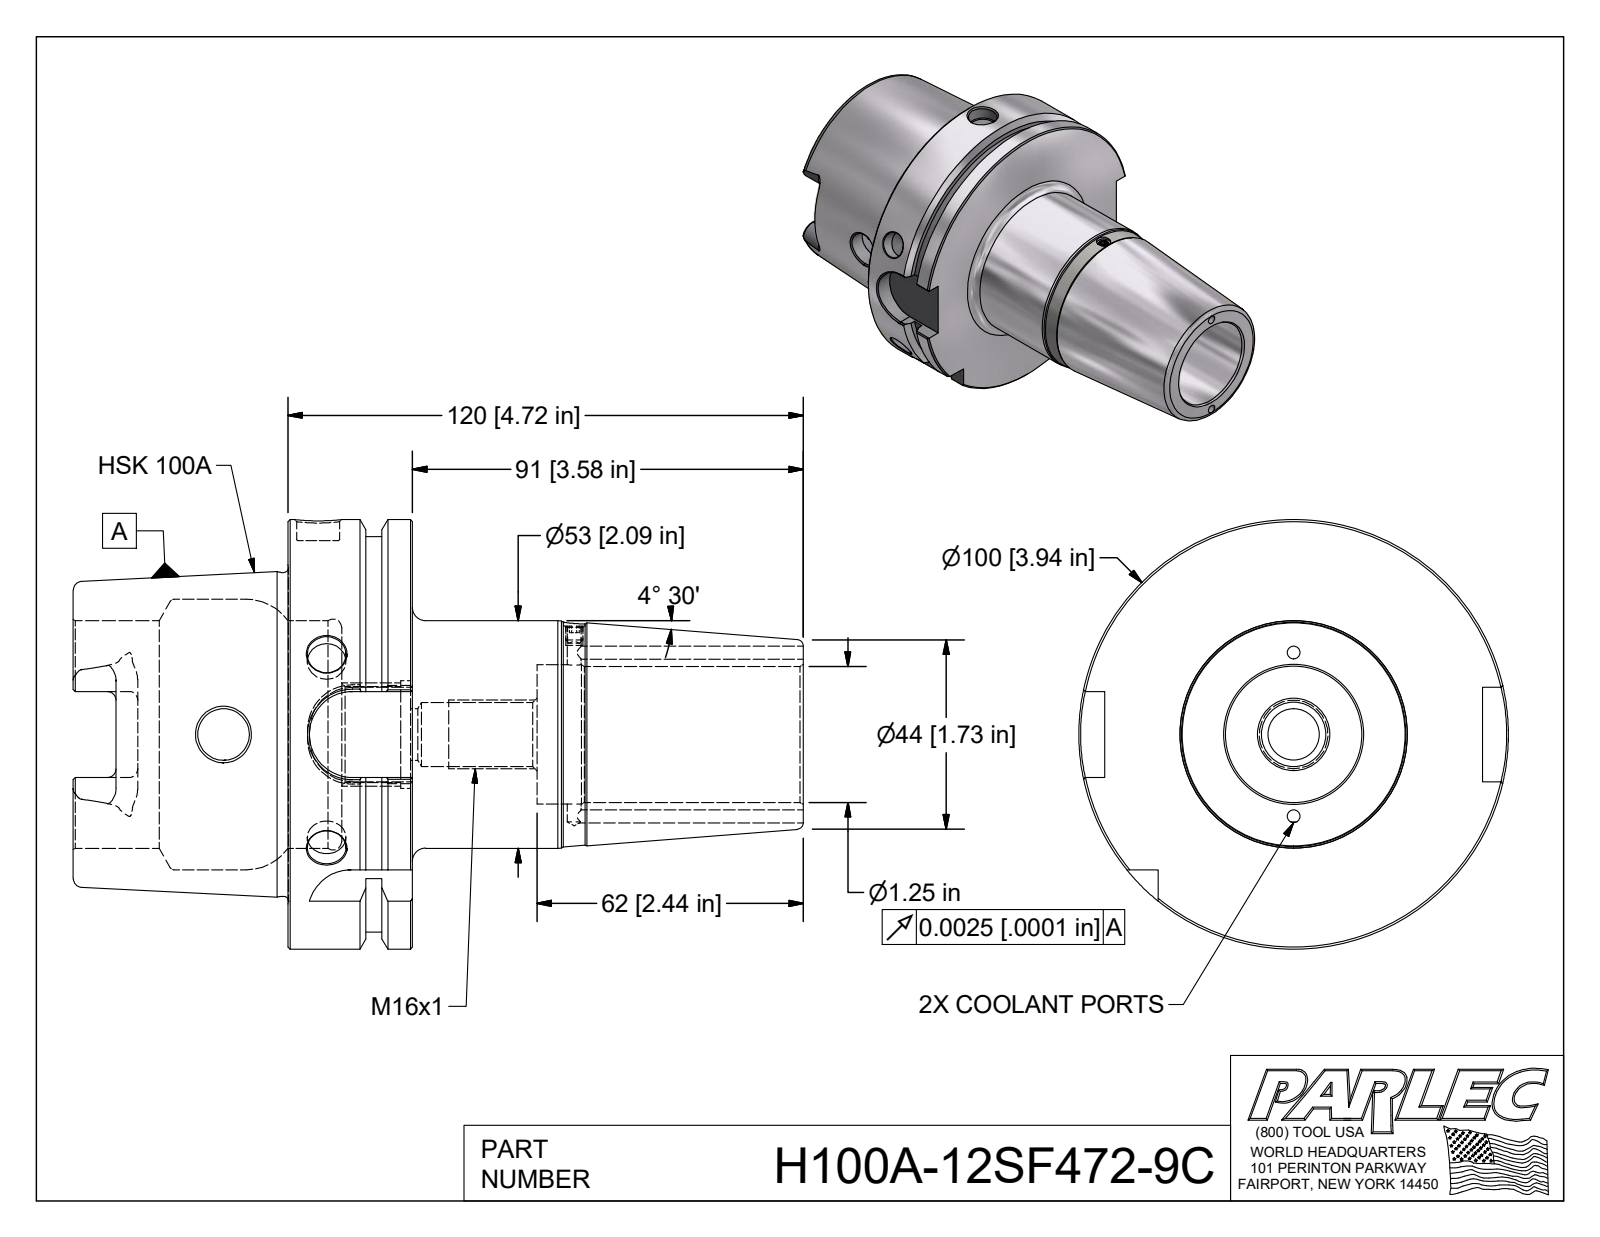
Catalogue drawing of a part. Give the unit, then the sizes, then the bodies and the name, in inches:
Units: inches
Overall size (bounding box): 6.693 × 3.937 × 3.937
Round holes (diameter × count): ⌀0.118 ×2, ⌀0.354 ×2, ⌀0.472 ×2, ⌀0.128 ×1, ⌀0.197 ×1, ⌀0.394 ×1, ⌀0.587 ×1, ⌀0.881 ×1, ⌀0.985 ×1, ⌀1.248 ×1, ⌀1.278 ×1, ⌀2.087 ×1
Round bosses / shafts (diameter × count): ⌀3.937 ×1, ⌀3.622 ×1, ⌀2.967 ×1
Partial cylindrical surfaces — rounded edges, fillets, slot ends (radius × count): R0.079 ×6, R0.192 ×4, R0.394 ×4
Main face-to-face distances: 1.142, 0.492, 0.65, 1.969, 2.461, 3.11, 4.252, 2.283, 1.791, 6.693
Hole centre spacings: 0.75, 1.5, 2.349
Volume: 23.15 in³ · Surface area: 111.4 in²
Bodies: 1 solid, 153 faces (49 planar, 42 cylindrical, 62 other)
STEP written by: Autodesk Inventor 2018 (AUTOMOTIVE_DESIGN)
